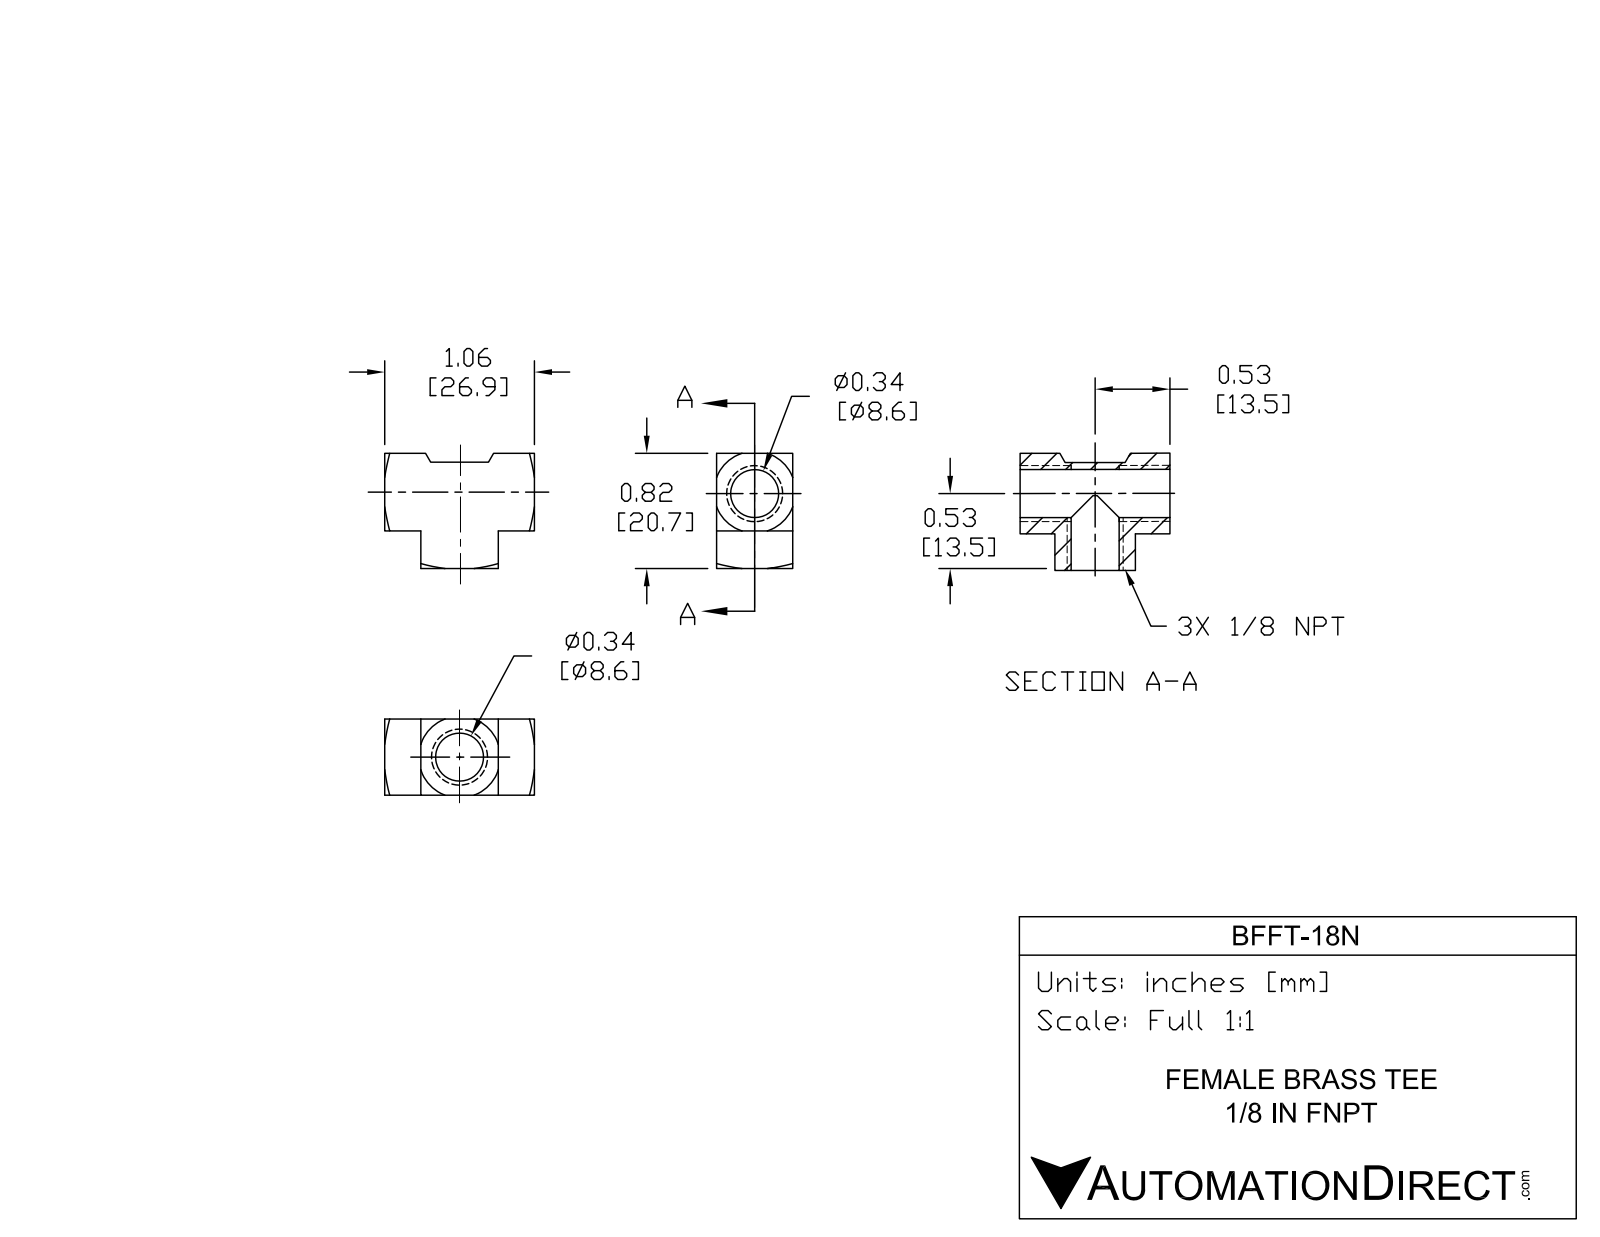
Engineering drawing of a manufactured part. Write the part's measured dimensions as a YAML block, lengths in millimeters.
part_name: "BFFT-18N"
step_written_by: "SolidWorks 2015 (CONFIG_CONTROL_DESIGN)"
units: millimeters
bodies: {solids: 1, faces: 32, planar: 16, cylindrical: 4, other: 12}
overall_size: [27.9, 21.1, 14.2]
volume: 4570
surface_area: 3152
round_holes:
  - {diameter: 8.6, count: 2}
face_to_face_distances: [14.2, 14.5, 6.7, 21.2, 1.7, 12.8, 27.9, 21.1, 19.4, 6.6]
